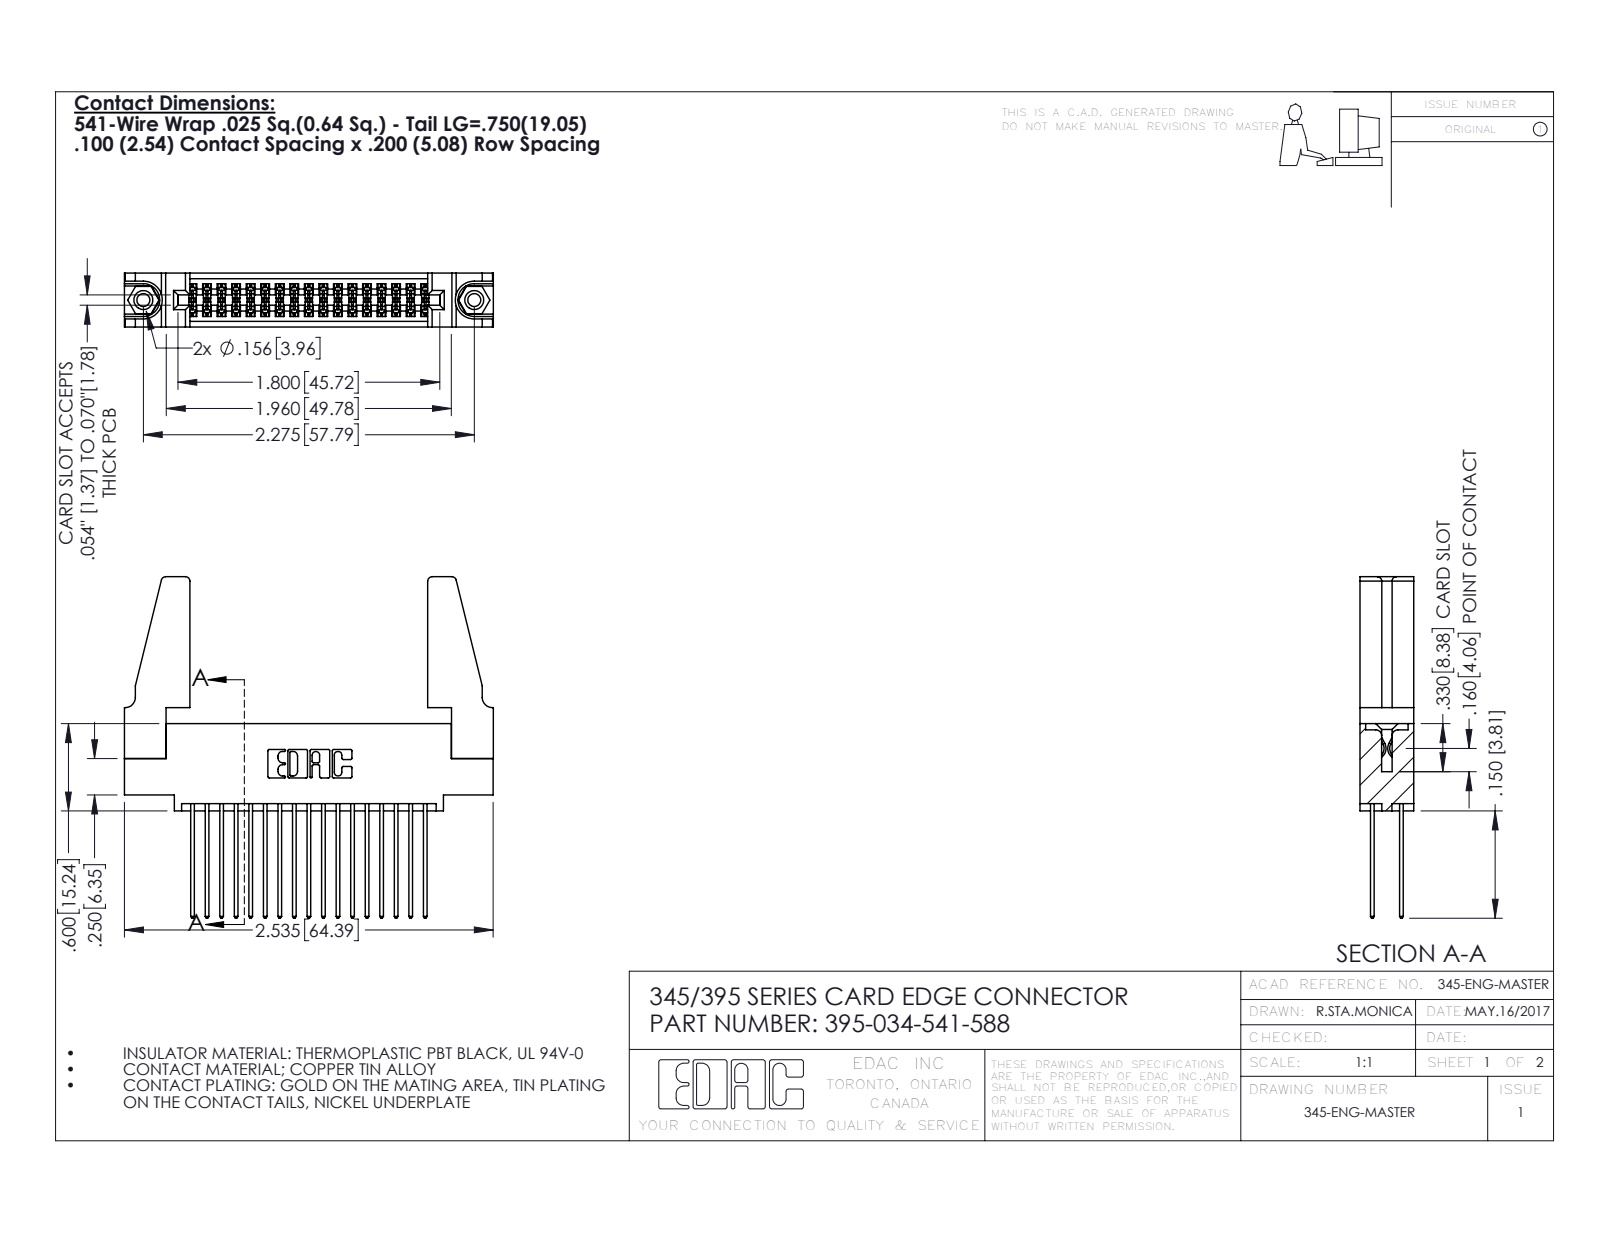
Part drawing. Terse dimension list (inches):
name: 345-250-001_345-250-001-102; 345 Part_0.110 Offset - 0.156 Dia-TH; 395-034-541-588; 345-292-001_345-293-141 (+1 more)
written by: SolidWorks 2016 (CONFIG_CONTROL_DESIGN)
unit: in
bodies: 39 solids, 1954 faces (1278 planar, 660 cylindrical, 16 other)
size: 2.536 × 2.347 × 0.37
volume: 0.574 in³; area: 19.74 in²
holes: 2× ⌀0.089, 2× ⌀0.125, 2× ⌀0.156, 1× ⌀0.064
bosses: 2× ⌀0.155
rounds: 51× R0.006, 34× R0.01, 22× R0.01, 8× R0.03, 6× R0.007, 6× R0.031, 3× R0.026, 2× R0.014
face distances: 0.072, 0.298, 0.37, 0.2, 0.098, 0.272, 0.025, 0.225, 0.175, 0.15
hole spacings: 0.27, 2.041, 2.275
